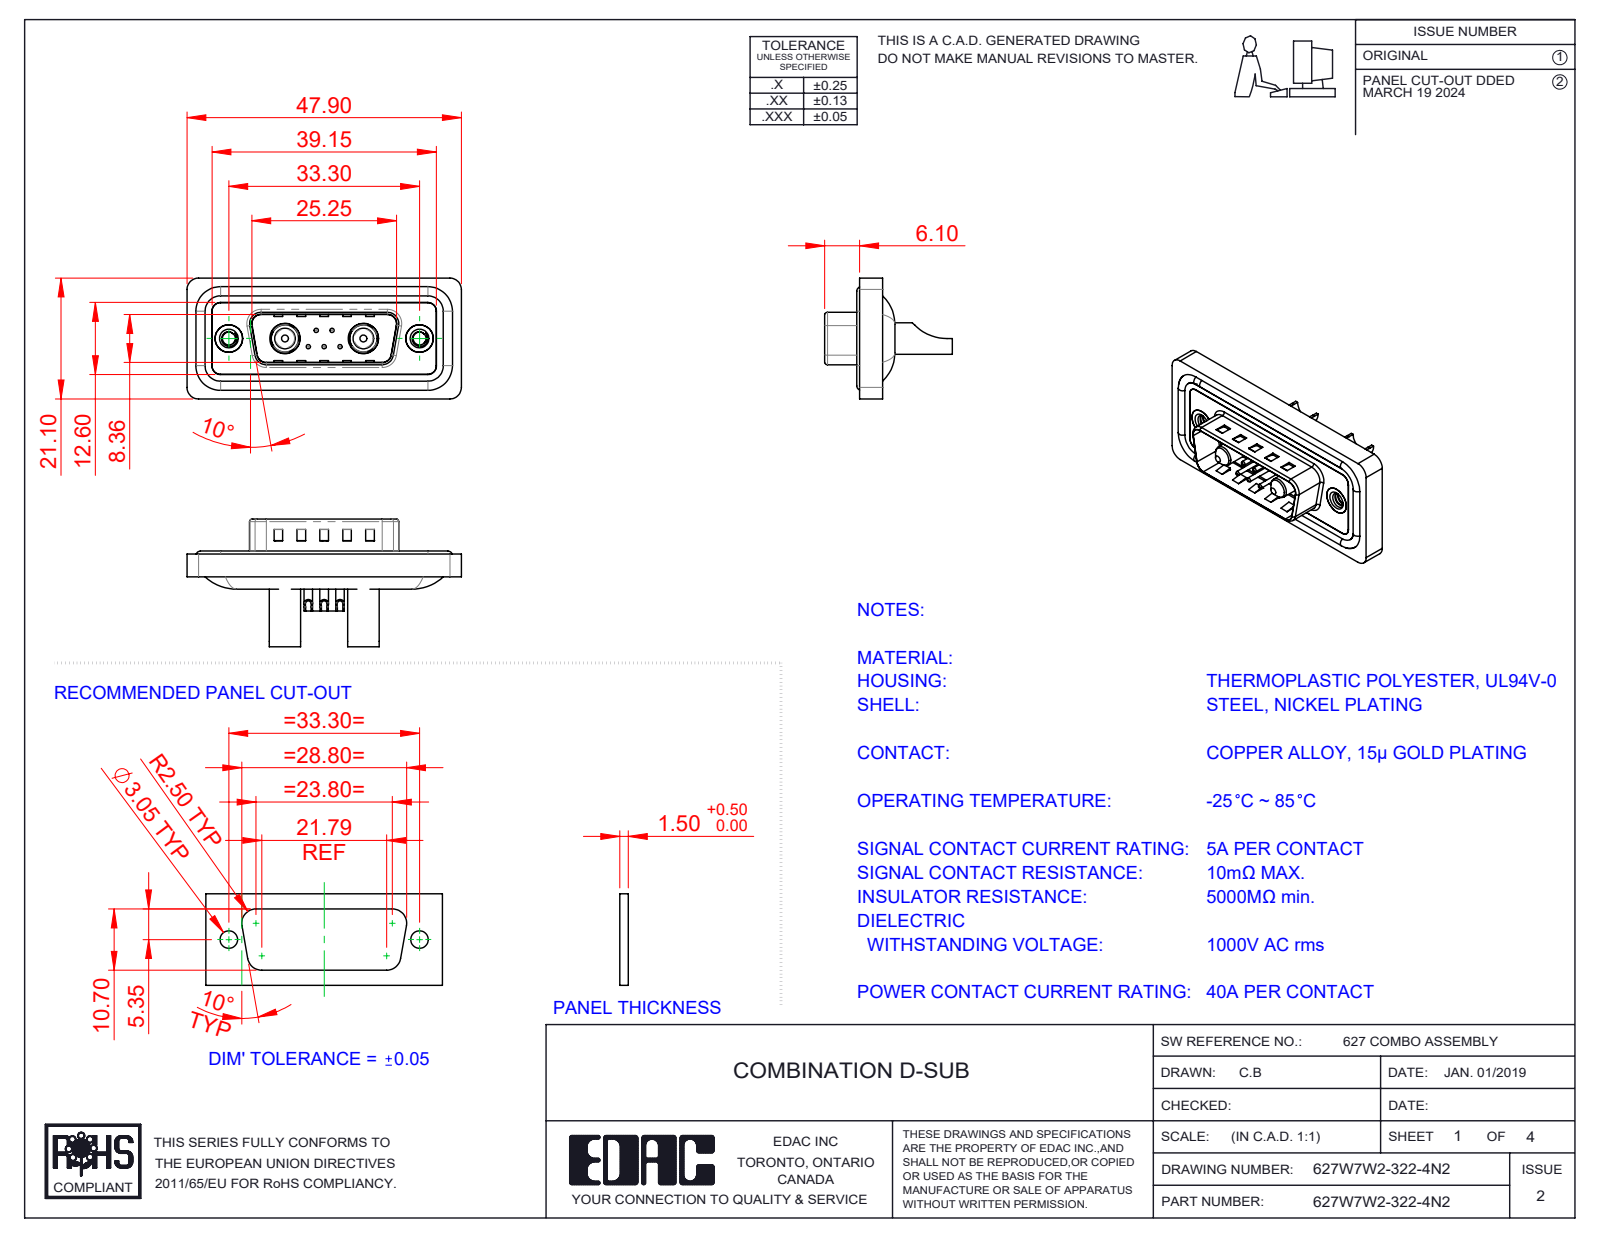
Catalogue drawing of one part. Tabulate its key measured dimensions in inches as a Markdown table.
| quantity | value |
| --- | --- |
| part name | 627Combo Waterproof Housing_15 Contacts; 627Combo Contact Row 2_22; 627W7W2-322-4N2; Power Pin_40A SC (+5 more) |
| STEP written by | SolidWorks 2023 (CONFIG_CONTROL_DESIGN) |
| units | inches |
| bodies | 16 solids, 718 faces (246 planar, 304 cylindrical, 168 other) |
| overall size | 1.886 × 0.878 × 0.831 |
| volume | 0.342 in³ |
| surface area | 14.12 in² |
| round holes (diameter × count) | 0.03 × 5, 0.039 × 5, 0.063 × 5, 0.079 × 5, 0.089 × 2, 0.157 × 2, 0.181 × 2, 0.189 × 2, 0.191 × 2, 0.197 × 2, 0.209 × 2 |
| round bosses / shafts (diameter × count) | 0.059 × 5, 0.063 × 4, 0.217 × 2, 0.205 × 2, 0.193 × 2, 0.187 × 2, 0.148 × 2, 0.142 × 2 |
| partial cylindrical surfaces (radius × count) | 0.059 × 26, 0.079 × 20, 0.02 × 8, 0.063 × 8, 0.039 × 6, 0.01 × 4, 0.024 × 4, 0.026 × 4 |
| main face-to-face distances | 0.016, 0.043, 0.063, 0.02, 0.059, 0.122, 0.114, 0.032, 0.377, 0.098 |
| hole center spacings | 0.124, 0.109, 0.386, 0.925, 0.17, 0.17, 0.198, 0.198 |
